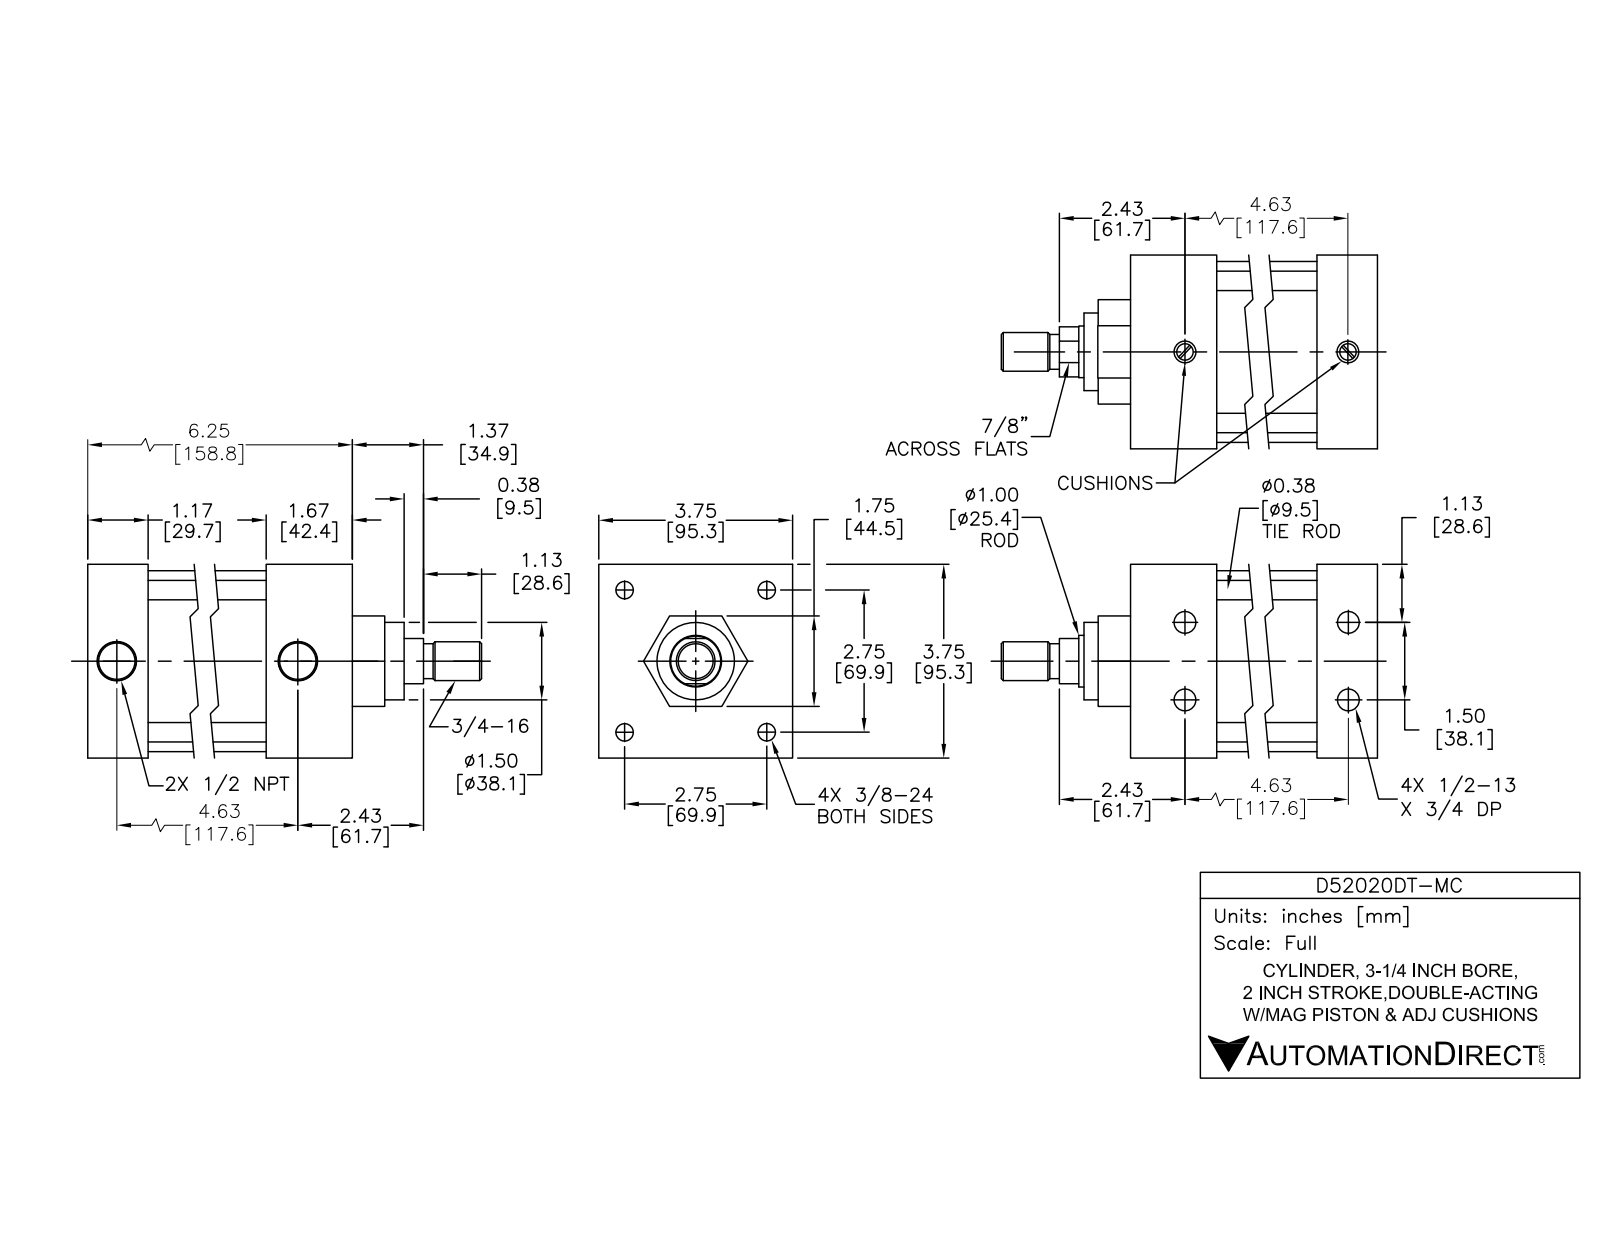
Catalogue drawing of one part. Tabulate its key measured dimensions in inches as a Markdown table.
| quantity | value |
| --- | --- |
| part name | D52020DT-M BODY; D52020DT-M PISTON; D52020DT-MC |
| STEP written by | SolidWorks 2015 (AUTOMOTIVE_DESIGN) |
| units | inches |
| bodies | 12 solids, 303 faces (99 planar, 114 cylindrical, 90 other) |
| overall size | 8.745 × 3.75 × 3.75 |
| volume | 58.77 in³ |
| surface area | 294.3 in² |
| round holes (diameter × count) | 0.33 × 4, 0.406 × 4, 0.417 × 4, 0.625 × 4, 0.5 × 2, 0.766 × 2, 1 × 1, 1.003 × 1, 3.25 × 1 |
| round bosses / shafts (diameter × count) | 0.609 × 4, 0.375 × 4, 0.34 × 4, 3.5 × 1, 3.247 × 1, 1.75 × 1, 0.997 × 1, 0.97 × 1 |
| partial cylindrical surfaces (radius × count) | 0.375 × 4 |
| main face-to-face distances | 3.75, 0.08, 3.326, 6.246, 1.75, 4.997, 1.249, 3.751, 1.246, 2.495 |
| hole center spacings | 0.75, 0.76, 1.5, 1.95, 1.95, 2.758, 2.758, 3.9 |
